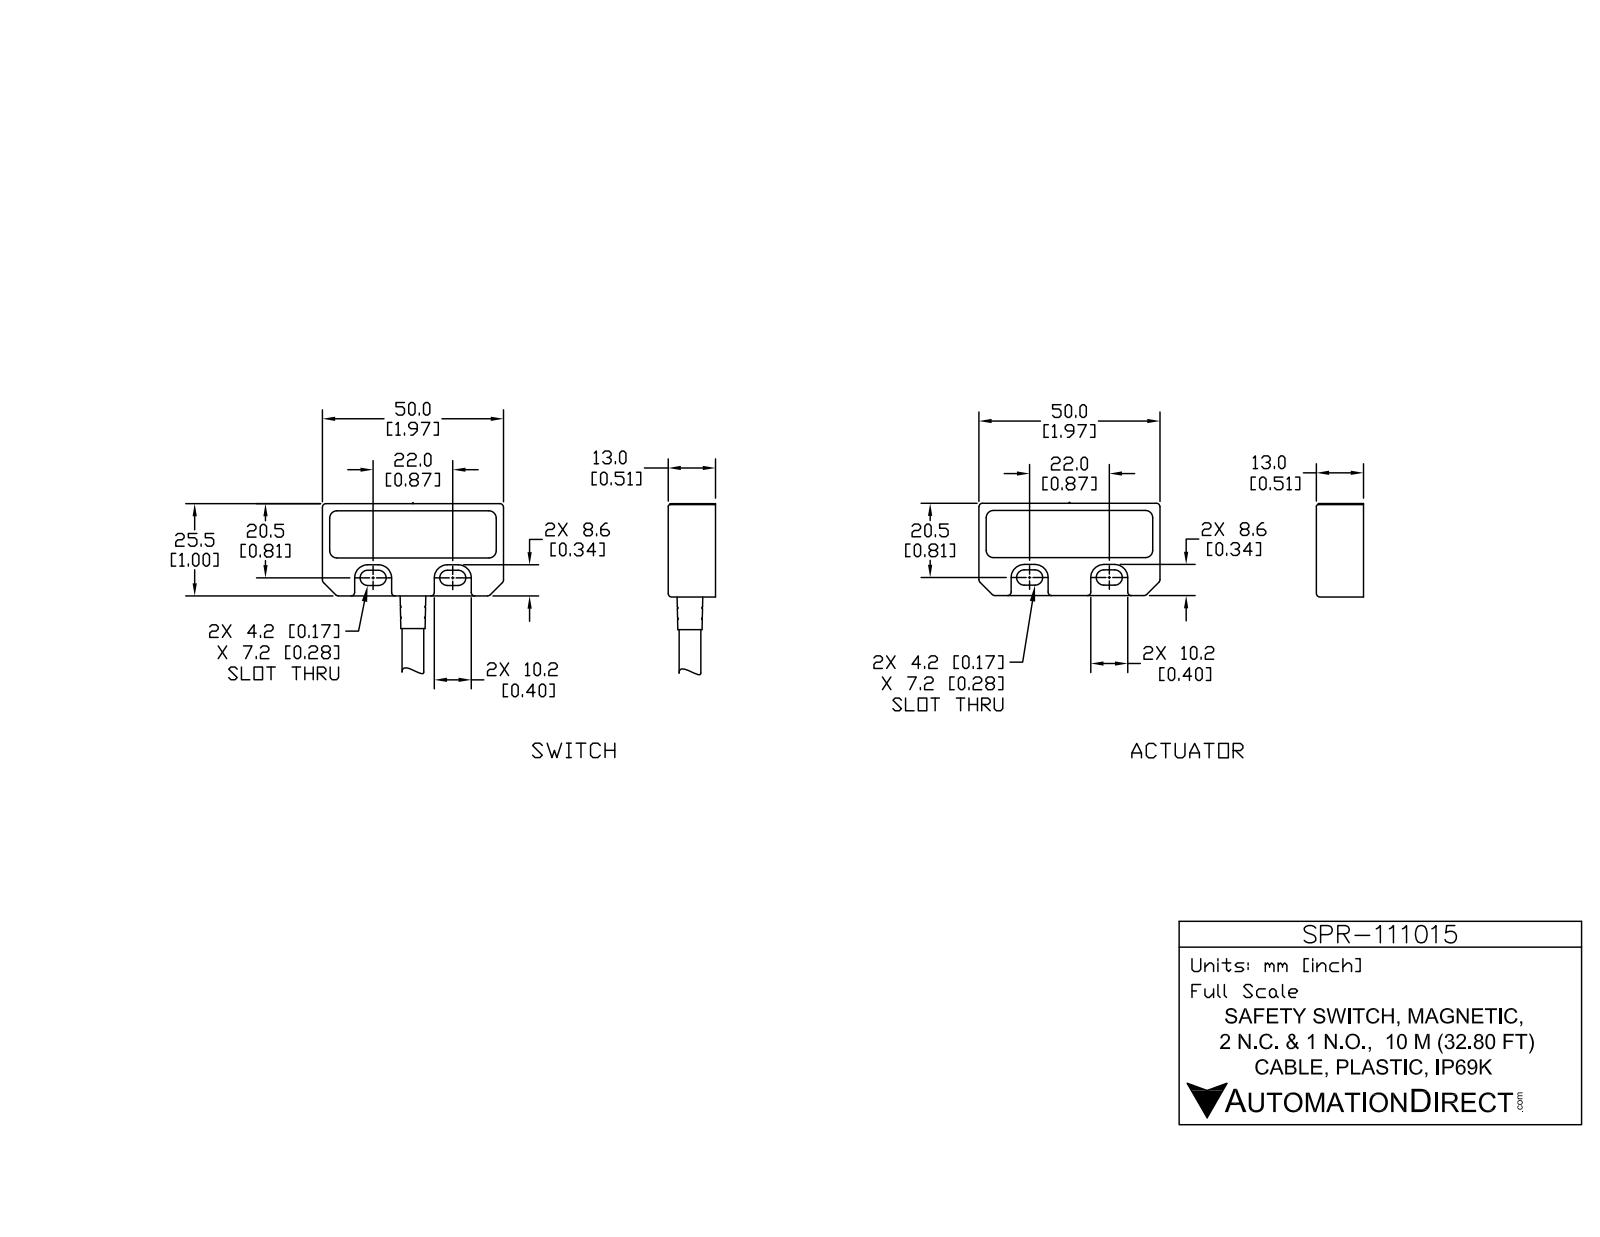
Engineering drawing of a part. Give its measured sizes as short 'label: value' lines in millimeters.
name: SPR-111015; SPR-111015_2; SPR-111015_1
written by: SolidWorks 2017 (AUTOMOTIVE_DESIGN)
unit: mm
bodies: 4 solids, 191 faces (61 planar, 80 cylindrical, 50 other)
size: 149.5 × 50 × 13.3
volume: 33 810 mm³; area: 11 750 mm²
bosses: 1× ⌀6
rounds: 36× R1, 8× R2, 8× R2.1, 8× R3.6, 2× R0.5
face distances: 13, 25.5, 26.5, 13.3, 1, 50, 52, 4.2, 4.5, 8.8
